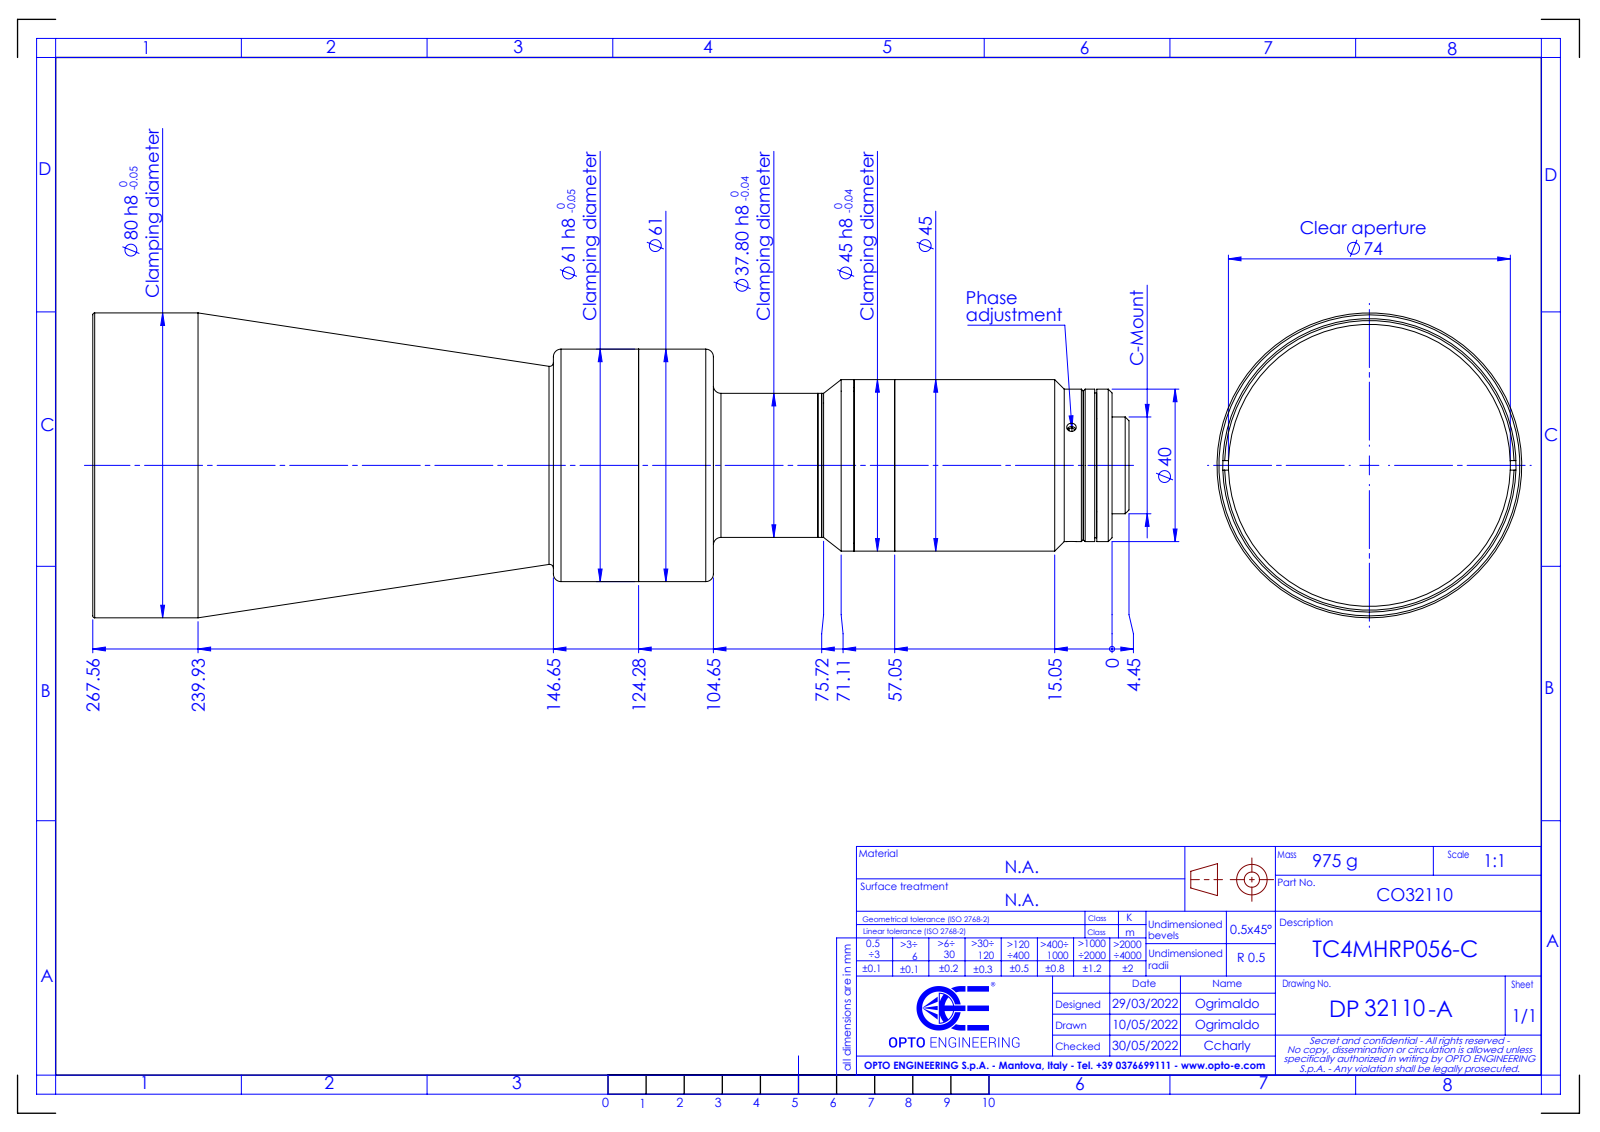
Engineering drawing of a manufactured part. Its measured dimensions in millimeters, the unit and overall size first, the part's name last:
Units: millimetres
Overall size (bounding box): 272 × 80 × 80
Round holes (diameter × count): ⌀2.5 ×3, ⌀22.5 ×1, ⌀53 ×1, ⌀74 ×1, ⌀77 ×1
Round bosses / shafts (diameter × count): ⌀80 ×1, ⌀61 ×1, ⌀45 ×1, ⌀40 ×1, ⌀37.8 ×1, ⌀25.4 ×1
Main face-to-face distances: 100.66, 100.11, 0.55, 104.66, 4.55, 4, 19.62, 119.73, 120.28, 124.28
Bodies: 0 solids, 98 faces (26 planar, 42 cylindrical, 30 other)
Part name (STEP PRODUCT): DP32110-A_TC4MHRP056-C
STEP written by: SolidWorks 2021 (CONFIG_CONTROL_DESIGN)
